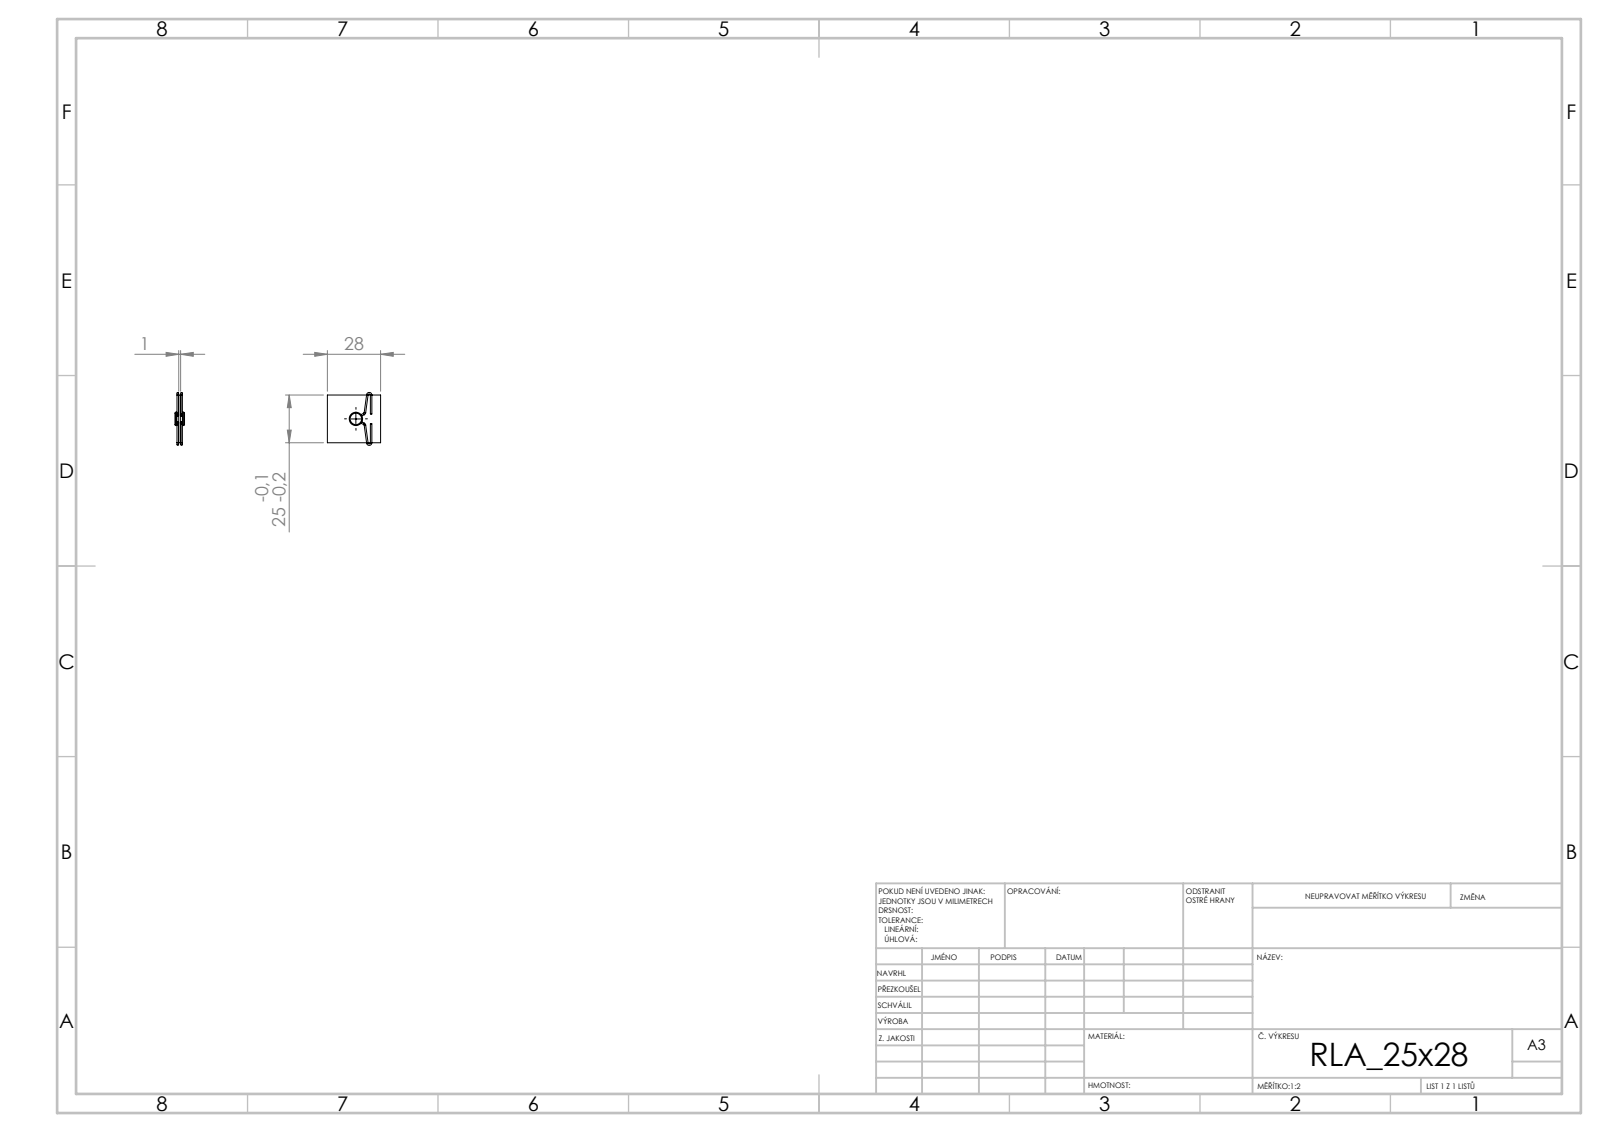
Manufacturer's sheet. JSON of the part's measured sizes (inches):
{"step_written_by": "SolidWorks 2019 (CONFIG_CONTROL_DESIGN)", "units": "inches", "bodies": {"solids": 3, "faces": 82, "planar": 14, "cylindrical": 40, "other": 28}, "overall_size": [1.102, 1.094, 0.197], "volume_in3": 0.053, "surface_area_in2": 3.086, "round_bosses_or_shafts": [[0.031, 14], [0.276, 1], [0.157, 1]], "face_to_face_distances": [0.039, 0.079, 0.118, 0.157, 0.197, 0.984, 1.102, 0.392, 0.593, 0.201]}
